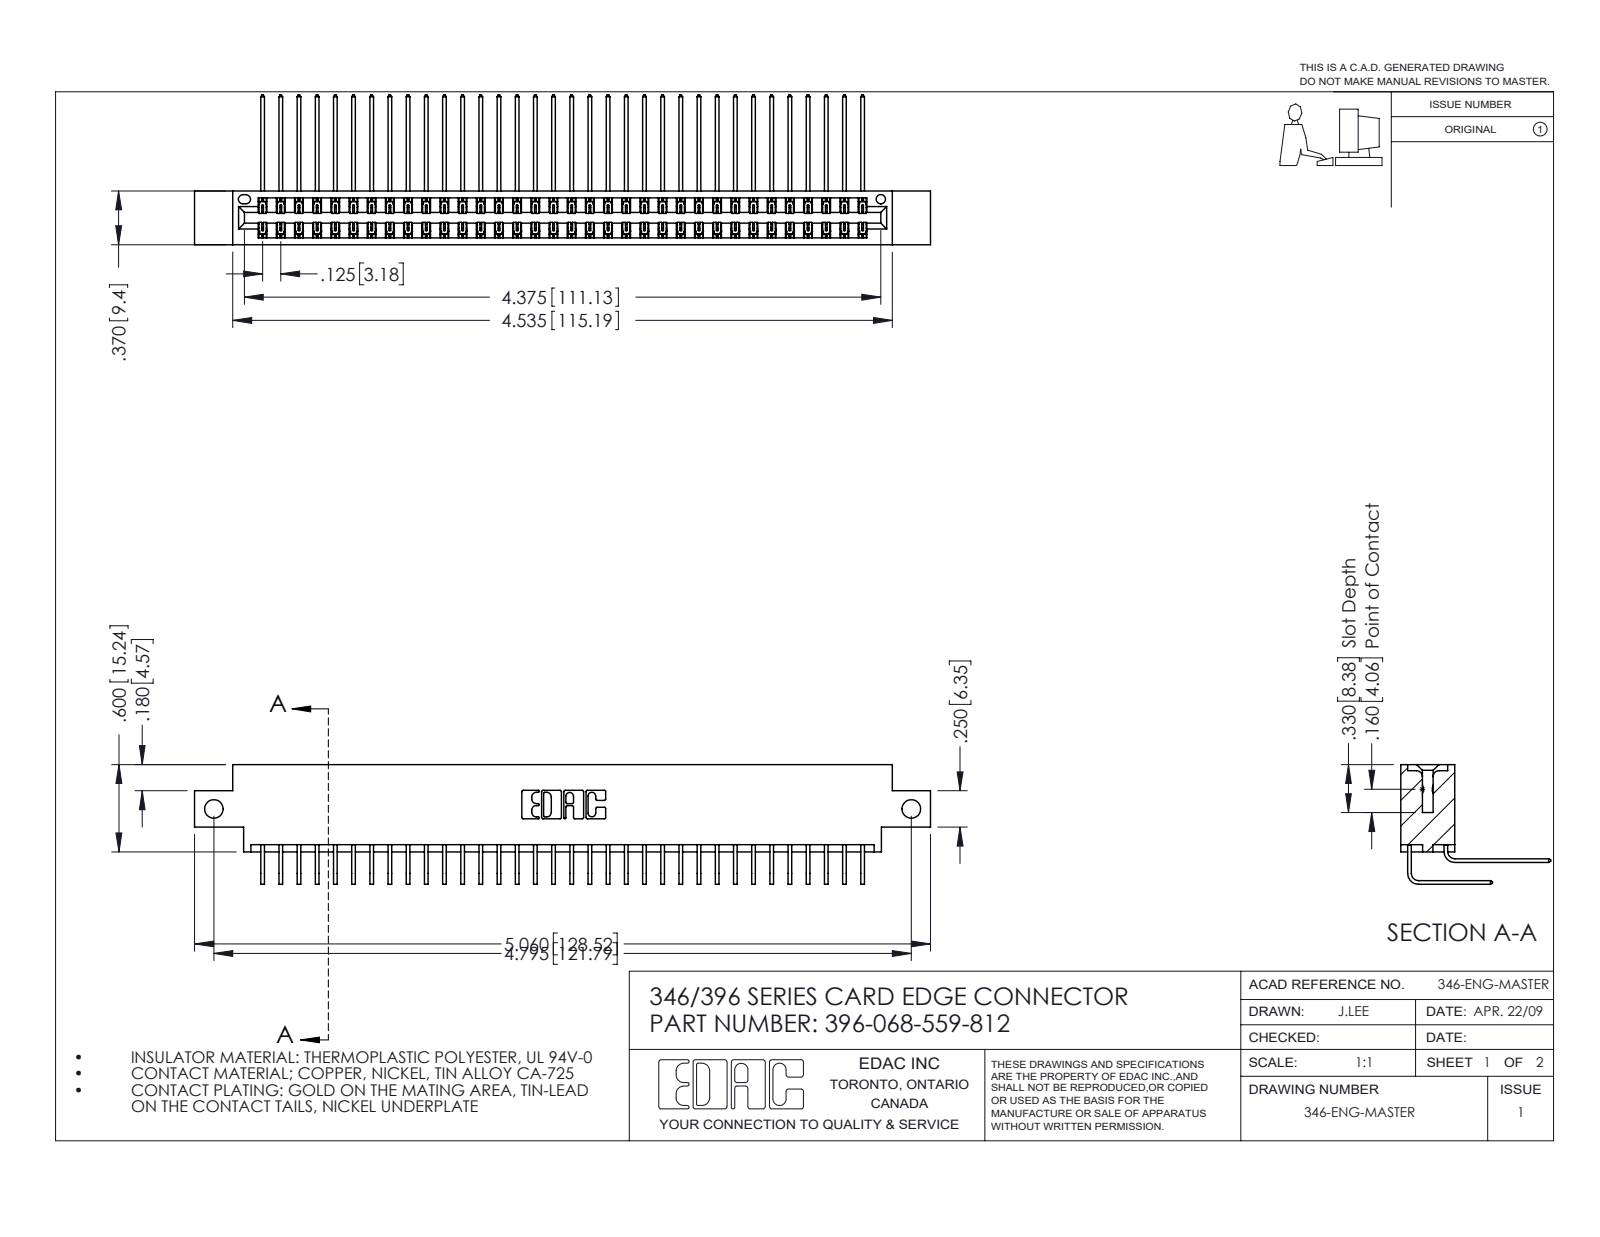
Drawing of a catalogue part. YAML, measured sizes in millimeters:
part_name: "396-068-559-812; 345-292-001_559 Tail - 2; 346 Part_0.170 Offset - Side Mount; 345-292-001_558 559 Tail - 1"
step_written_by: "SolidWorks 2016 (CONFIG_CONTROL_DESIGN)"
units: millimeters
bodies: {solids: 69, faces: 3798, planar: 2596, cylindrical: 1202, other: 0}
overall_size: [128.5, 26.2, 20.9]
volume: 12600
surface_area: 19150
round_holes:
  - {diameter: 3.3, count: 2}
  - {diameter: 1.6, count: 1}
partial_cylinders:
  - {radius: 0.2, count: 102}
  - {radius: 0.3, count: 22}
  - {radius: 0.2, count: 6}
  - {radius: 0.8, count: 6}
  - {radius: 0.7, count: 3}
  - {radius: 0.4, count: 2}
  - {radius: 0.6, count: 2}
  - {radius: 0.6, count: 2}
face_to_face_distances: [1.2, 8.2, 0.6, 9.4, 6.4, 1.8, 7.6, 7, 3.8, 5.6]
hole_center_spacings: [121.8]
